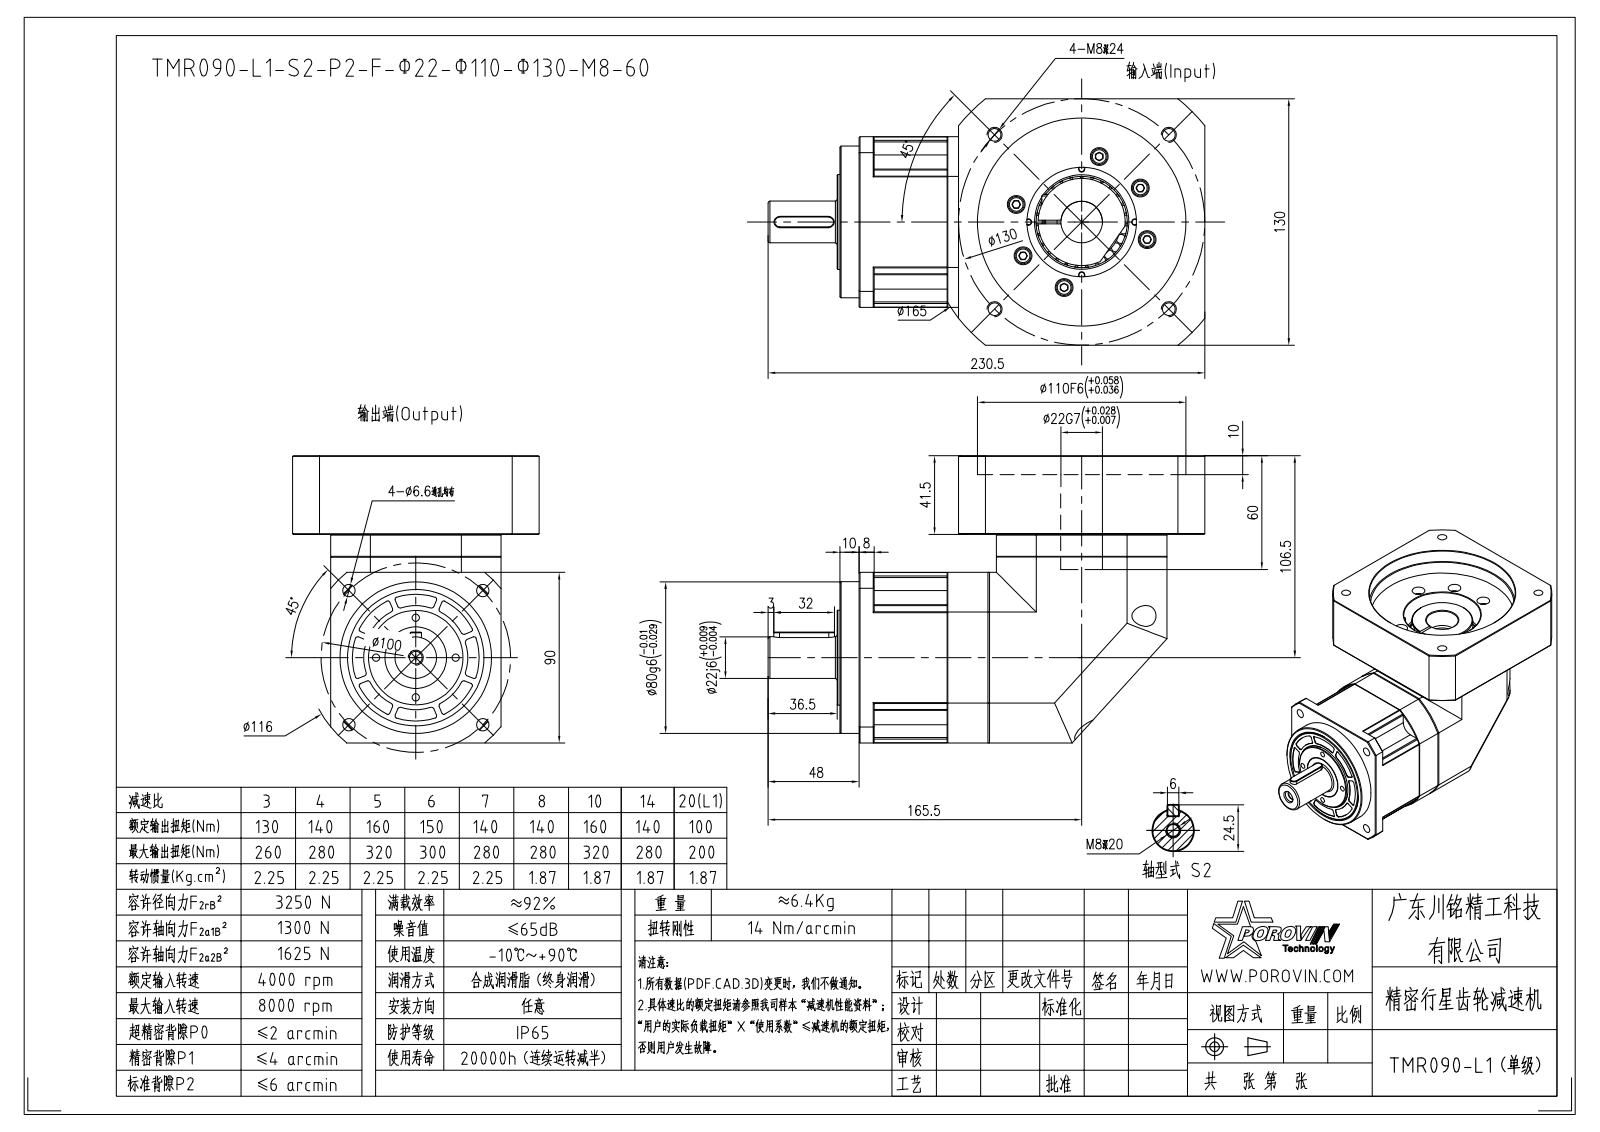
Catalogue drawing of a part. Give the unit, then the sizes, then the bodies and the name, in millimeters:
Units: millimetres
Overall size (bounding box): 230.5 × 151.5 × 130
Round holes (diameter × count): ⌀5.4 ×12, ⌀9.5 ×12, ⌀4.2 ×7, ⌀5.5 ×6, ⌀6.5 ×5, ⌀6.8 ×5, ⌀4 ×4, ⌀6.6 ×4, ⌀6.68 ×4, ⌀8 ×4, ⌀11 ×4, ⌀5 ×1
Round bosses / shafts (diameter × count): ⌀8.5 ×12, ⌀8 ×12, ⌀5 ×12, ⌀10 ×4, ⌀9.88 ×4, ⌀6 ×4, ⌀80 ×1, ⌀55 ×1
Partial cylindrical surfaces — rounded edges, fillets, slot ends (radius × count): R1 ×92, R7.5 ×4, R51 ×3, R3 ×2, R4 ×1, R5.25 ×1, R50.25 ×1, R58 ×1
Main face-to-face distances: 20, 110, 21.5, 41.5, 90, 12, 21.3, 130, 53.5, 5
Hole centre spacings: 35.75, 27.36, 38.16, 66.06, 66.53, 31.84, 81.89, 61.92
Volume: 1 640 000 mm³ · Surface area: 246 659 mm²
Bodies: 42 solids, 1268 faces (509 planar, 542 cylindrical, 217 other)
Part name (STEP PRODUCT): HEXAGON_SOCKET_HEAD_CAP_S-14123; 40X50X500_1; HEXAGON_SOCKET_HEAD_CAP_S-14176; TMR900003_1 (+8 more)
STEP written by: CREO PARAMETRIC BY PTC INC, 2020053 (CONFIG_CONTROL_DESIGN)
